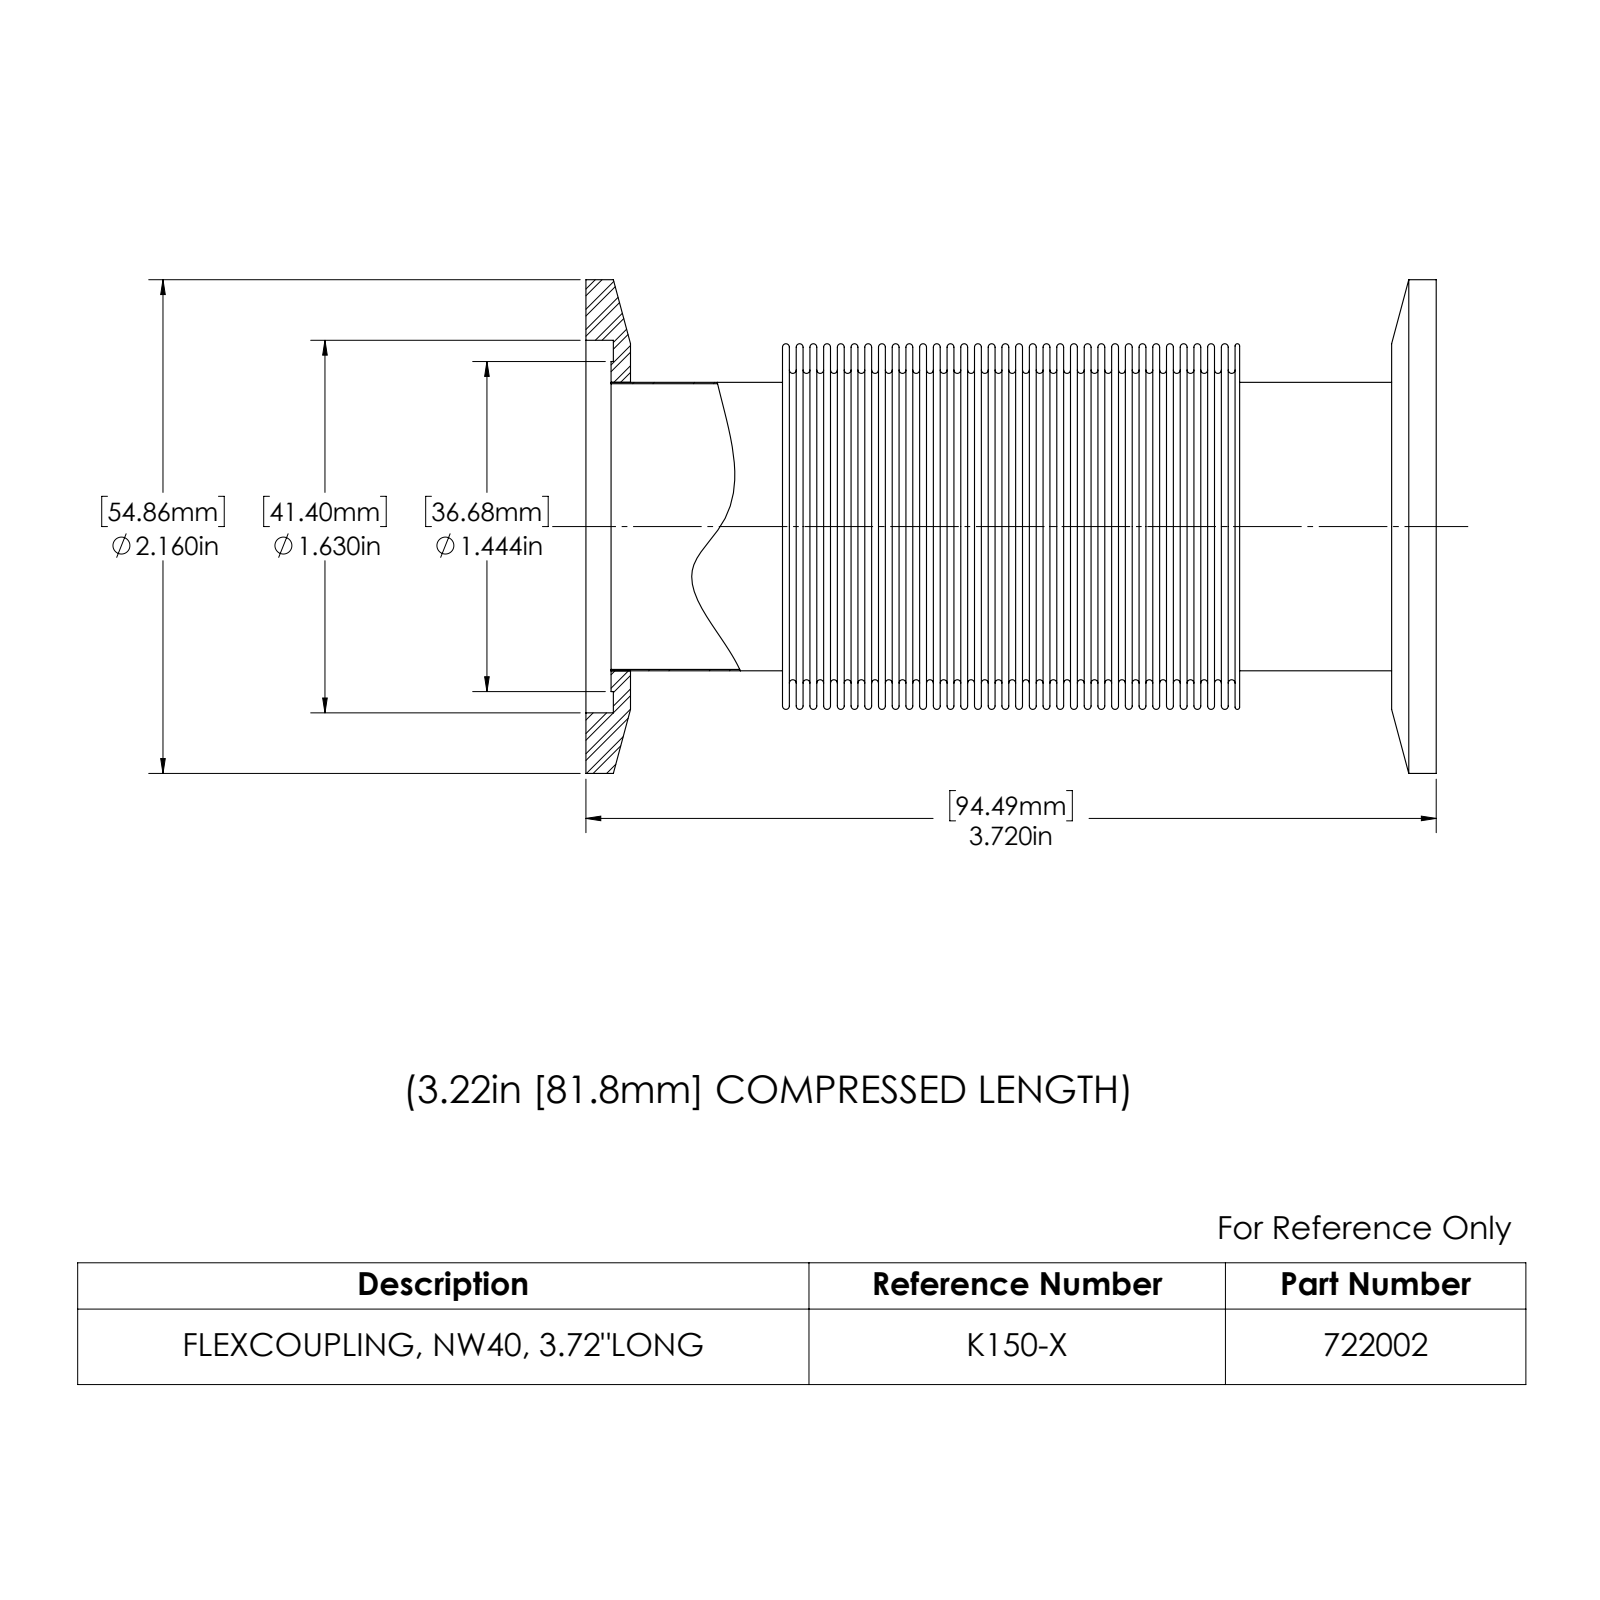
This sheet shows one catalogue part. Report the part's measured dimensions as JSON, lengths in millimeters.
{"part_name": "722002_B", "step_written_by": "SolidWorks 2022 (CONFIG_CONTROL_DESIGN)", "units": "millimeters", "bodies": {"solids": 3, "faces": 574, "planar": 146, "cylindrical": 24, "other": 404}, "overall_size": [94.5, 54.9, 54.9], "volume_mm3": 15300, "surface_area_mm2": 75870, "round_holes": [[31.8, 1], [32.1, 1], [41.4, 1]], "round_bosses_or_shafts": [[54.9, 1], [36.7, 1]], "face_to_face_distances": [1.5, 4.6, 3, 7.6, 94.5, 5, 89.5, 22, 72.5, 17]}
